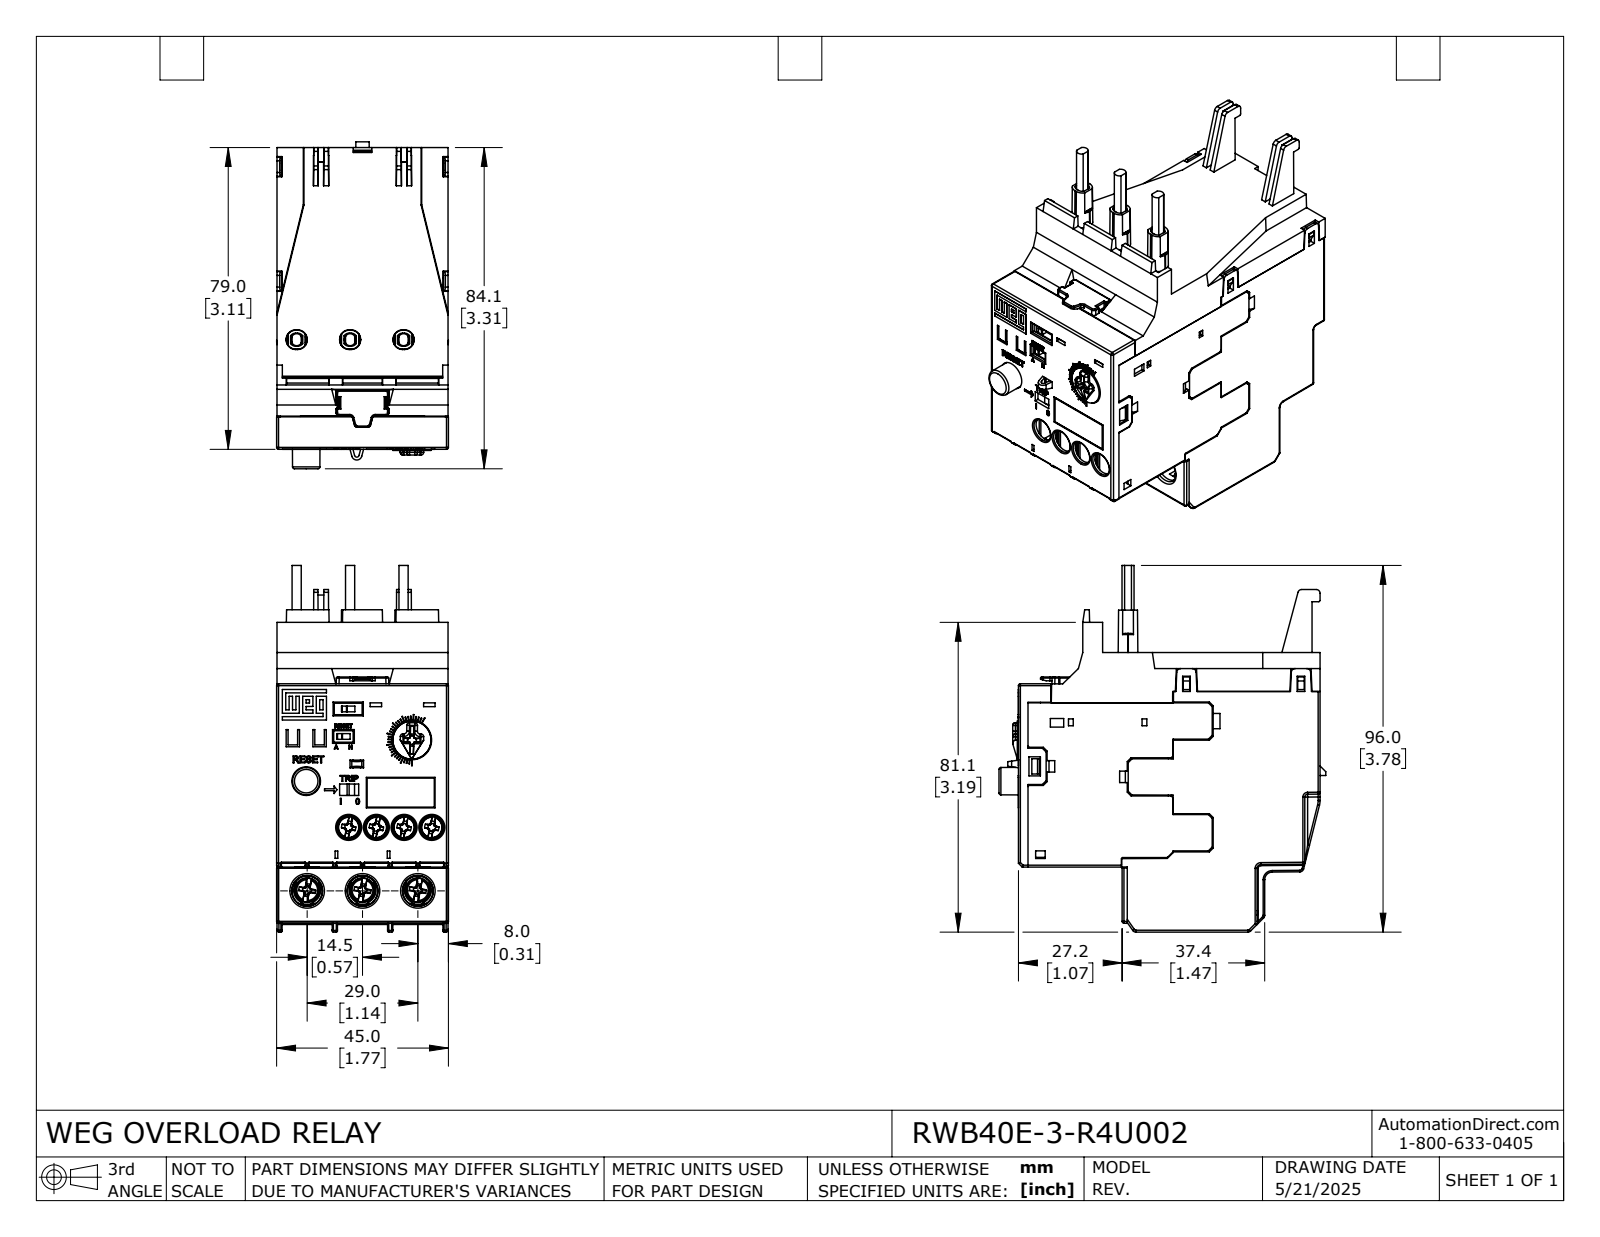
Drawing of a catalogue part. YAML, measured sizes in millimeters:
part_name: "RWB40E-3-R4U002"
step_written_by: "SolidWorks 2024 (AUTOMOTIVE_DESIGN)"
units: millimeters
bodies: {solids: 38, faces: 3774, planar: 2406, cylindrical: 808, other: 560}
overall_size: [96, 85.6, 45]
volume: 165500
surface_area: 74000
round_holes:
  - {diameter: 3, count: 9}
  - {diameter: 2.6, count: 6}
  - {diameter: 2.5, count: 4}
  - {diameter: 2.9, count: 3}
  - {diameter: 4.4, count: 3}
  - {diameter: 7.5, count: 1}
  - {diameter: 10.3, count: 1}
round_bosses_or_shafts:
  - {diameter: 3.5, count: 7}
  - {diameter: 2.2, count: 4}
  - {diameter: 7.5, count: 3}
  - {diameter: 4.2, count: 3}
  - {diameter: 2.9, count: 3}
  - {diameter: 2.5, count: 3}
partial_cylinders:
  - {radius: 0.3, count: 216}
  - {radius: 0.5, count: 76}
  - {radius: 1, count: 55}
  - {radius: 0.2, count: 43}
  - {radius: 0.3, count: 17}
  - {radius: 0.9, count: 17}
  - {radius: 0.4, count: 16}
  - {radius: 1.5, count: 14}
face_to_face_distances: [44.8, 7.3, 14.5, 1.2, 1, 6.2, 21.8, 10.2, 1.1, 13.5]
hole_center_spacings: [7.3, 14.5, 16.8, 21.8, 14, 14.5, 16.8, 19.7]
